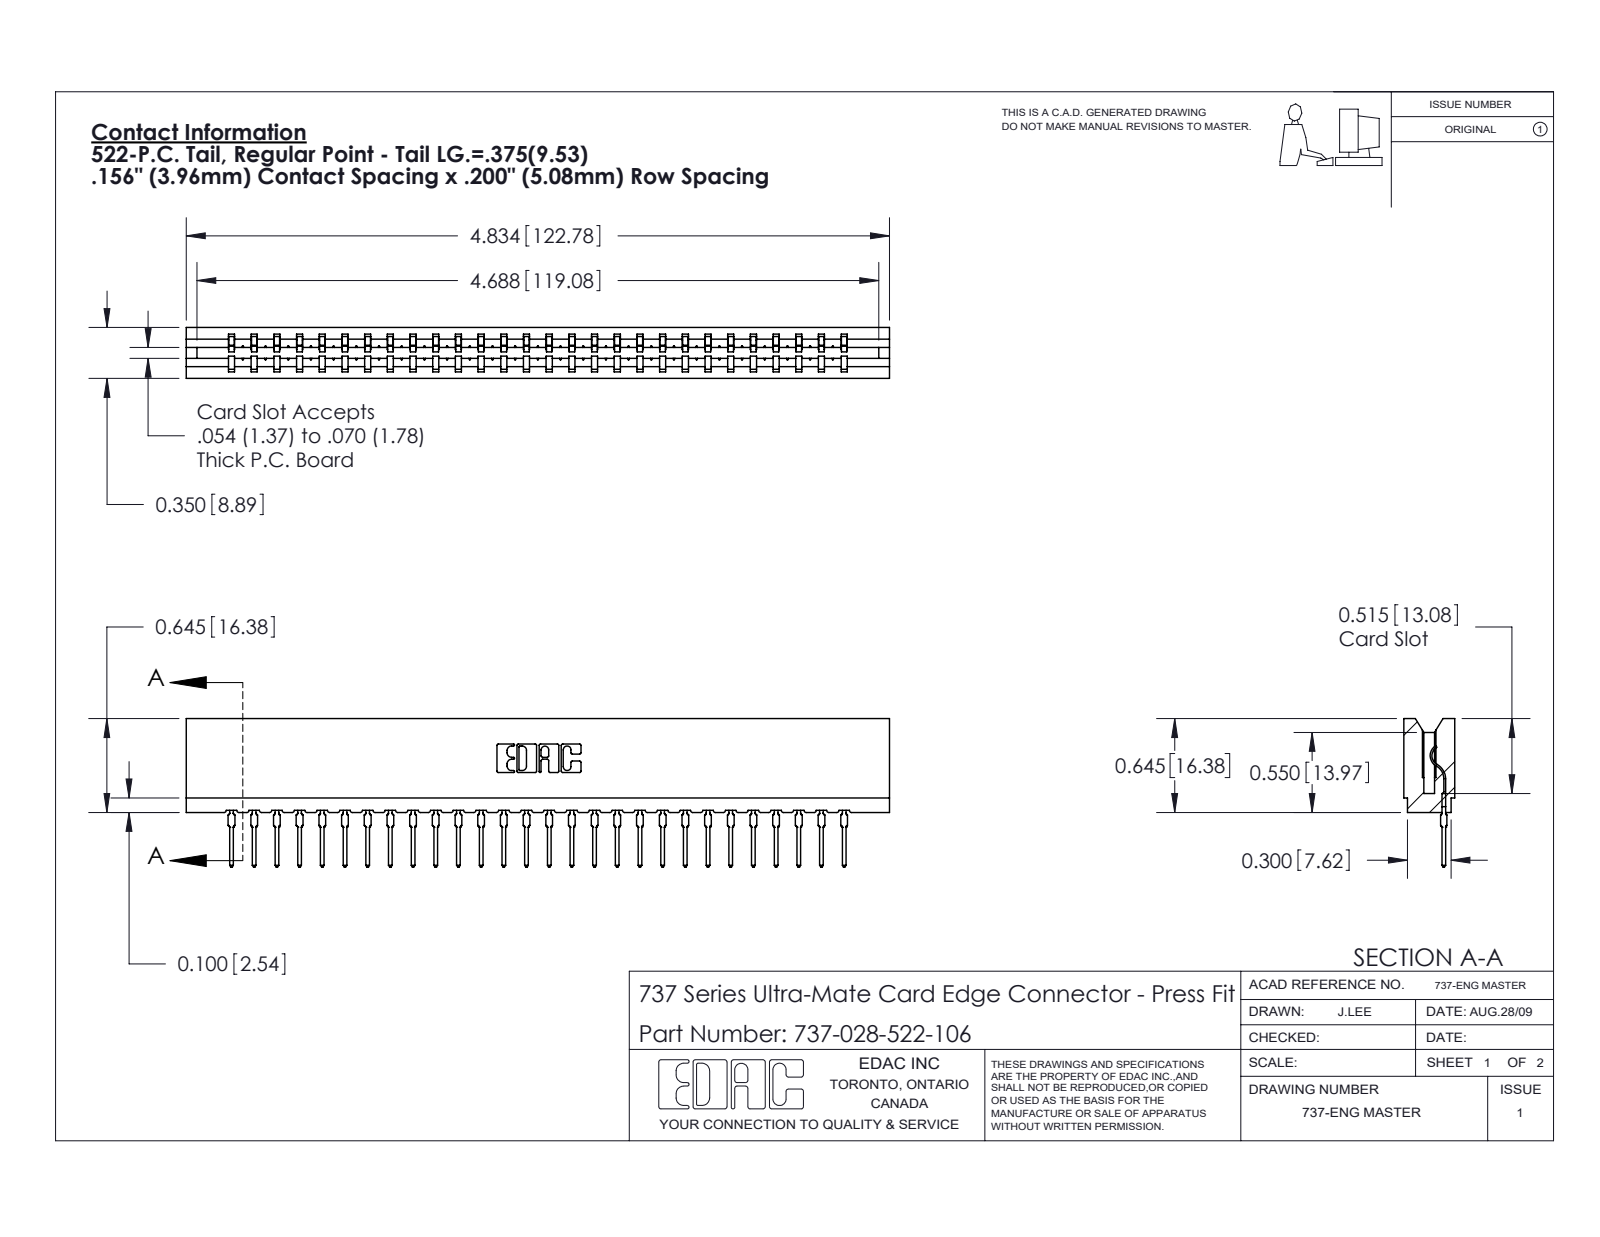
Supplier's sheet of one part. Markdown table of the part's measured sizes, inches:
| quantity | value |
| --- | --- |
| part name | 737 Part_Insulator Option - 06; 745-292-001_522; 737-028-522-106 |
| STEP written by | SolidWorks 2020 (CONFIG_CONTROL_DESIGN) |
| units | inches |
| bodies | 29 solids, 3259 faces (1959 planar, 572 cylindrical, 728 other) |
| overall size | 4.834 × 1.021 × 0.35 |
| volume | 0.73 in³ |
| surface area | 24.63 in² |
| partial cylindrical surfaces (radius × count) | 0.015 × 56, 0.021 × 56, 0.01 × 22, 0.007 × 6, 0.031 × 6, 0.005 × 4, 0.011 × 4, 0.026 × 3 |
| main face-to-face distances | 0.138, 0.212, 0.35, 0.074, 0.156, 0.045, 0.305, 0.093, 0.167, 0.624 |
